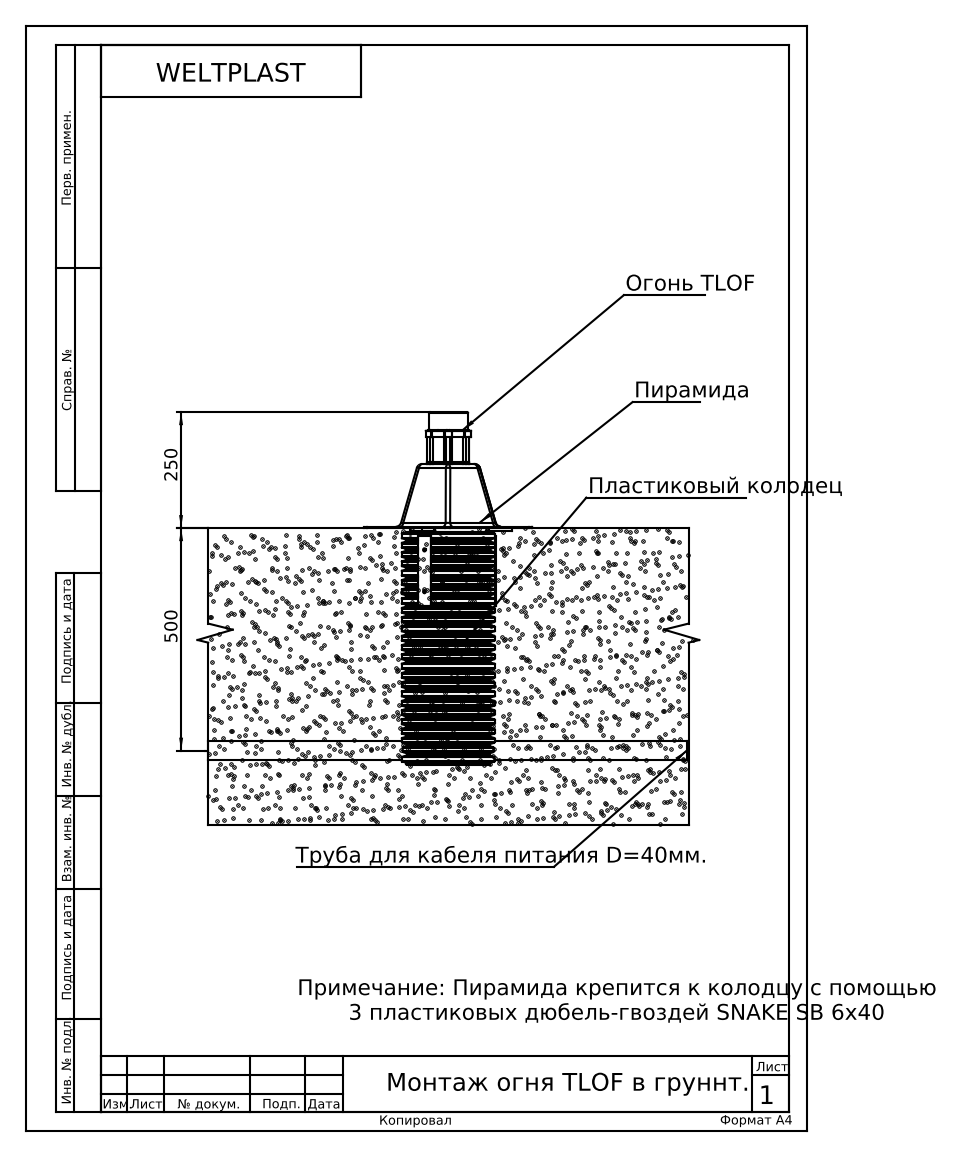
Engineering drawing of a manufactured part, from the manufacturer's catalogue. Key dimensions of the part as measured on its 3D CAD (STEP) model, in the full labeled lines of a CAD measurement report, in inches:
Part name (STEP PRODUCT): Втулка байонет; Сборка фонаря байонет; Провод 25; Сборка пирамиды байонет (+8 more)
STEP written by: SolidWorks 2018 (AUTOMOTIVE_DESIGN)
Units: inches
Bodies: 41 solids, 1955 faces (626 planar, 805 cylindrical, 524 other)
Overall size (bounding box): 40.496 × 29.852 × 16.219
Volume: 257.8 in³ · Surface area: 2 382 in²
Round holes (diameter × count): ⌀0.173 ×6, ⌀0.177 ×6, ⌀0.236 ×6, ⌀0.256 ×6, ⌀0.197 ×5, ⌀0.209 ×4, ⌀0.157 ×3, ⌀0.165 ×2, ⌀0.496 ×2, ⌀0.797 ×2, ⌀1.024 ×1, ⌀1.575 ×1
Round bosses / shafts (diameter × count): ⌀0.299 ×6, ⌀0.197 ×3, ⌀0.157 ×3, ⌀0.846 ×2, ⌀0.776 ×2, ⌀0.591 ×2, ⌀7.874 ×1, ⌀7.087 ×1
Partial cylindrical surfaces — rounded edges, fillets, slot ends (radius × count): R0.079 ×28, R0.472 ×26, R0.197 ×25, R0.177 ×18, R0.039 ×16, R0.059 ×14, R0.118 ×12, R0.276 ×9
Main face-to-face distances: 0.118, 0.059, 0.236, 0.079, 2.539, 0.512, 0.827, 0.748, 0.591, 5.315
Hole centre spacings: 1.87, 3.239, 1.621, 1.893, 2.198, 1.665, 3.543, 3.74
